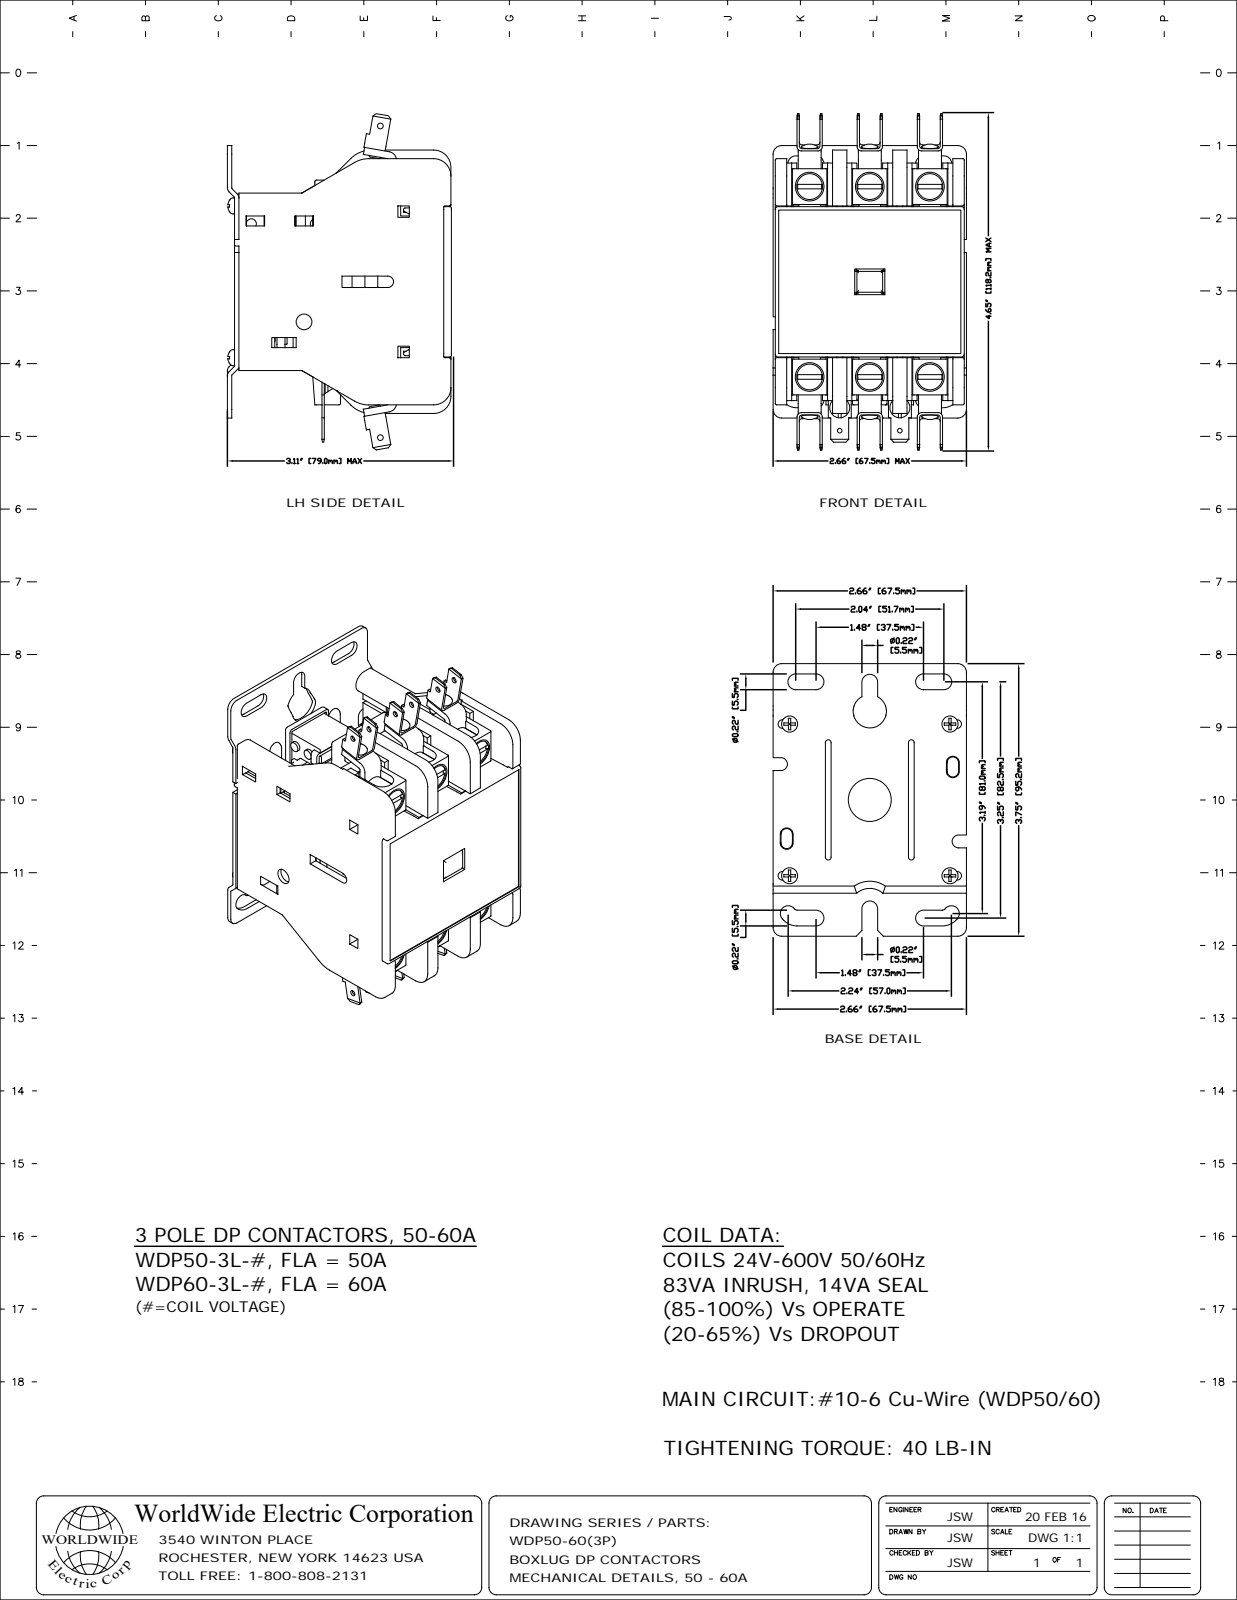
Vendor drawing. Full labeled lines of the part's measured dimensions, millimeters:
Part name (STEP PRODUCT): WDP60-3L-24
STEP written by: SolidWorks 2017 (AUTOMOTIVE_DESIGN)
Units: millimetres
Bodies: 5 solids, 3094 faces (1931 planar, 804 cylindrical, 359 other)
Overall size (bounding box): 95.2 × 73 × 67.5
Volume: 134 700 mm³ · Surface area: 97 680 mm²
Round holes (diameter × count): ⌀2.4 ×10, ⌀5 ×5, ⌀1.8 ×4, ⌀3.8 ×3, ⌀2 ×2, ⌀7 ×2, ⌀11.6 ×1, ⌀15 ×1
Round bosses / shafts (diameter × count): ⌀3.5 ×12, ⌀5.6 ×10, ⌀5 ×9, ⌀3.8 ×9, ⌀6.5 ×6, ⌀6.2 ×6, ⌀9 ×2, ⌀5.4 ×2
Partial cylindrical surfaces — rounded edges, fillets, slot ends (radius × count): R0.5 ×178, R1 ×55, R2 ×52, R1.5 ×31, R0.8 ×18, R2.7 ×16, R1.2 ×10, R2.3 ×6
Main face-to-face distances: 4, 1.5, 1, 19, 62, 16, 2.5, 36, 15, 39
Hole centre spacings: 20, 12, 18, 21.5, 21.5, 23.7, 26.6, 27.6
